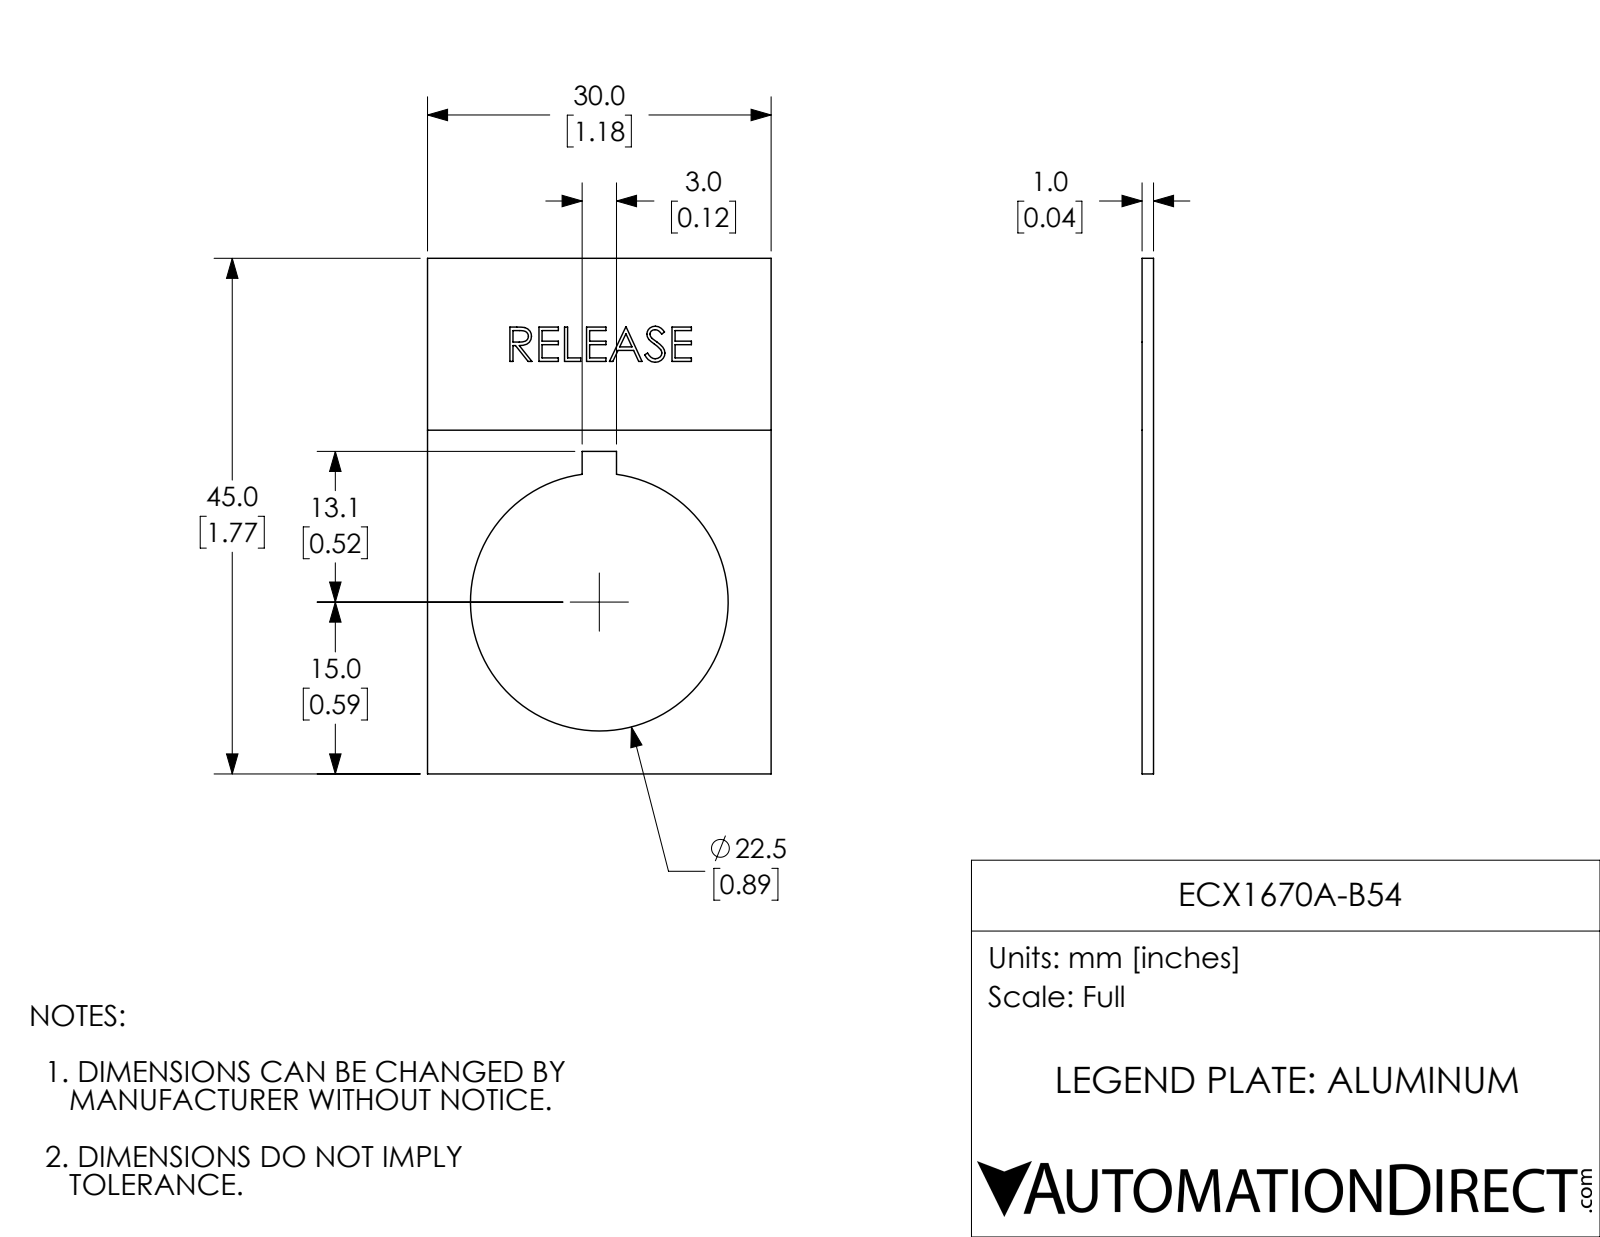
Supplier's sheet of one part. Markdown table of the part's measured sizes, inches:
| quantity | value |
| --- | --- |
| part name | ECX1670A-B54 |
| STEP written by | SolidWorks 2017 (AUTOMOTIVE_DESIGN) |
| units | inches |
| bodies | 1 solid, 108 faces (85 planar, 3 cylindrical, 20 other) |
| overall size | 1.772 × 1.181 × 0.039 |
| volume | 0.058 in³ |
| surface area | 3.287 in² |
| round holes (diameter × count) | 0.886 × 1 |
| main face-to-face distances | 0.039, 1.181, 1.772, 0.038, 0.531, 0.65, 1.108, 0.663, 0.118, 0.012 |
